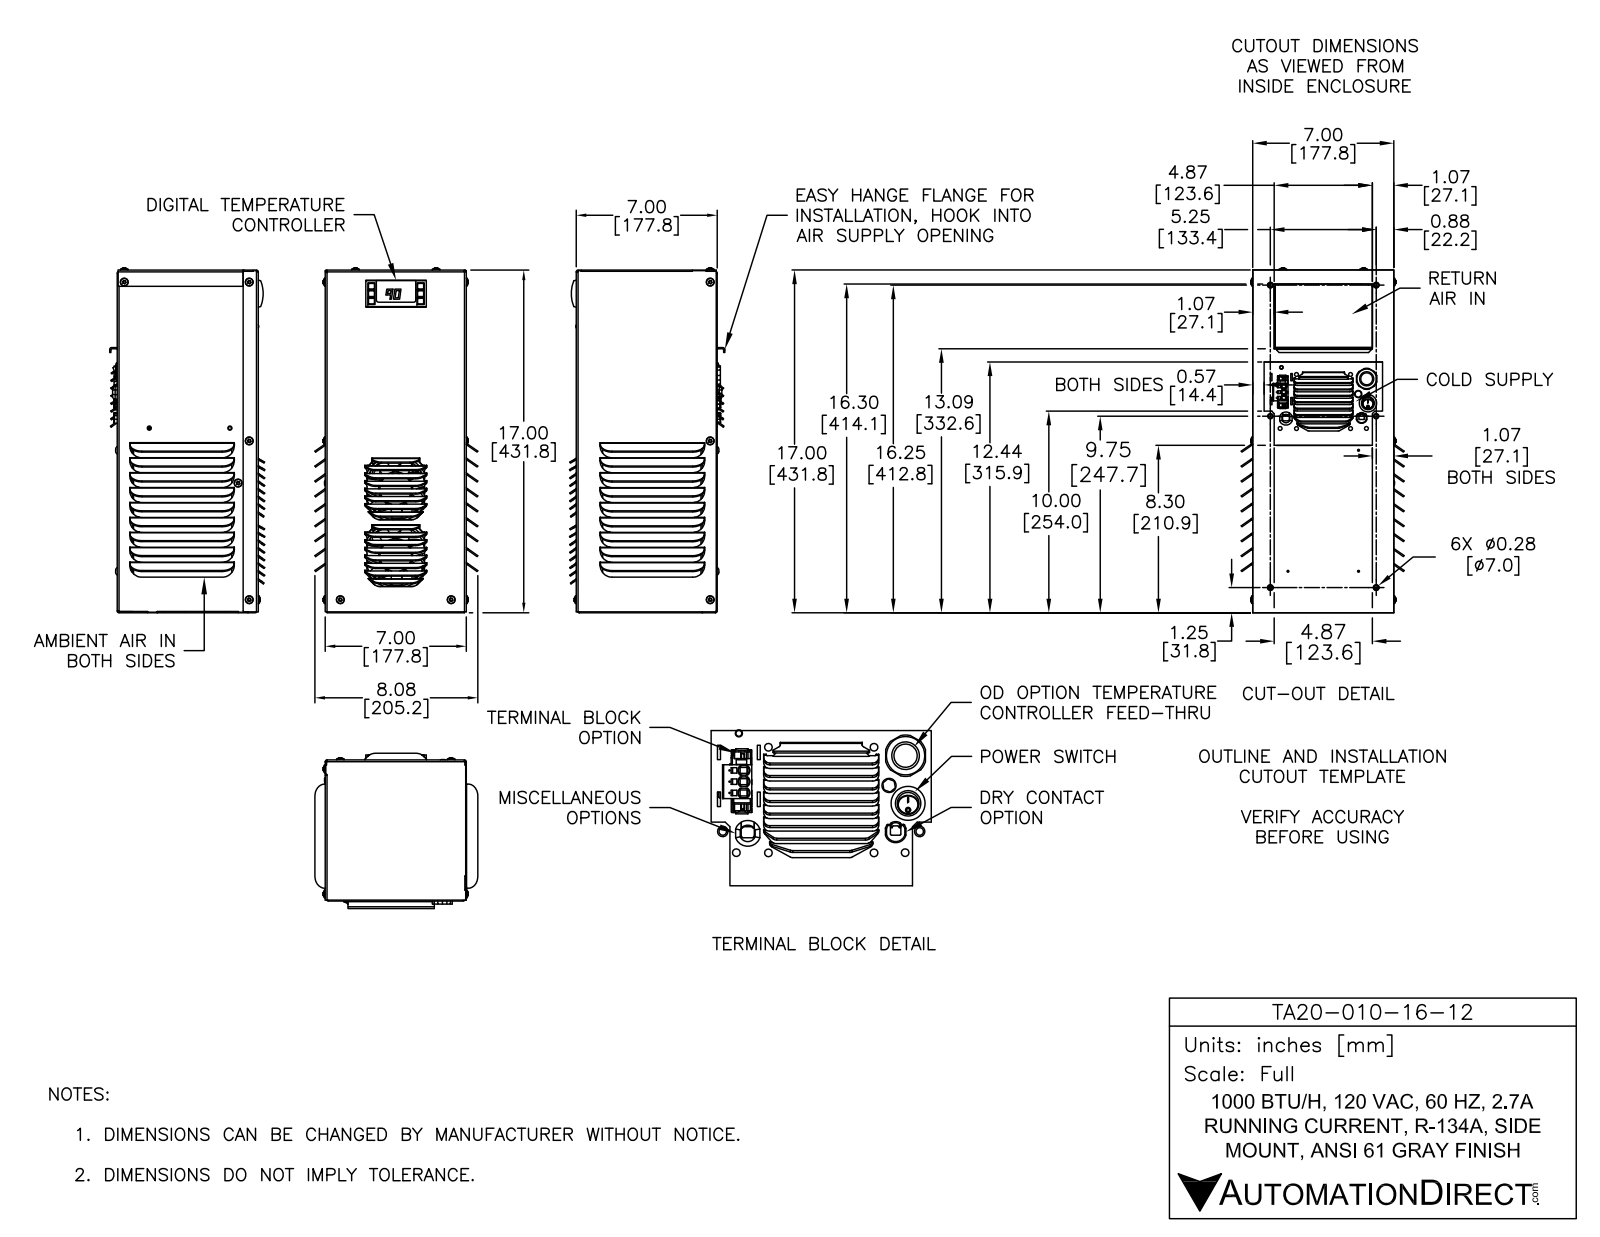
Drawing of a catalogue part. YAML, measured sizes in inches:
part_name: "TA20-010-16-12"
step_written_by: "SolidWorks 2019 (AUTOMOTIVE_DESIGN)"
units: inches
bodies: {solids: 70, faces: 3570, planar: 1682, cylindrical: 1401, other: 487}
overall_size: [17.092, 8.079, 7.704]
volume: 93.28
surface_area: 1758
round_holes:
  - {diameter: 0.203, count: 16}
  - {diameter: 0.325, count: 16}
  - {diameter: 0.33, count: 16}
  - {diameter: 0.28, count: 14}
  - {diameter: 0.219, count: 10}
  - {diameter: 0.193, count: 8}
  - {diameter: 0.2, count: 6}
  - {diameter: 0.201, count: 6}
  - {diameter: 0.272, count: 6}
  - {diameter: 0.109, count: 5}
  - {diameter: 0.195, count: 4}
  - {diameter: 0.156, count: 2}
round_bosses_or_shafts:
  - {diameter: 0.19, count: 17}
  - {diameter: 0.329, count: 14}
  - {diameter: 0.313, count: 10}
  - {diameter: 0.564, count: 6}
  - {diameter: 0.44, count: 6}
  - {diameter: 0.344, count: 6}
  - {diameter: 0.326, count: 6}
  - {diameter: 0.321, count: 6}
partial_cylinders:
  - {radius: 0.01, count: 100}
  - {radius: 0.125, count: 91}
  - {radius: 0.005, count: 90}
  - {radius: 0.031, count: 81}
  - {radius: 0.015, count: 77}
  - {radius: 0.091, count: 57}
  - {radius: 0.03, count: 53}
  - {radius: 0.594, count: 36}
face_to_face_distances: [0.06, 6.938, 0.06, 6.998, 6.935, 6.875, 6.875, 6.815, 6.878, 16.938]
hole_center_spacings: [0.8, 1, 1.601, 1.625, 1.25, 2, 2.359, 1.94]
